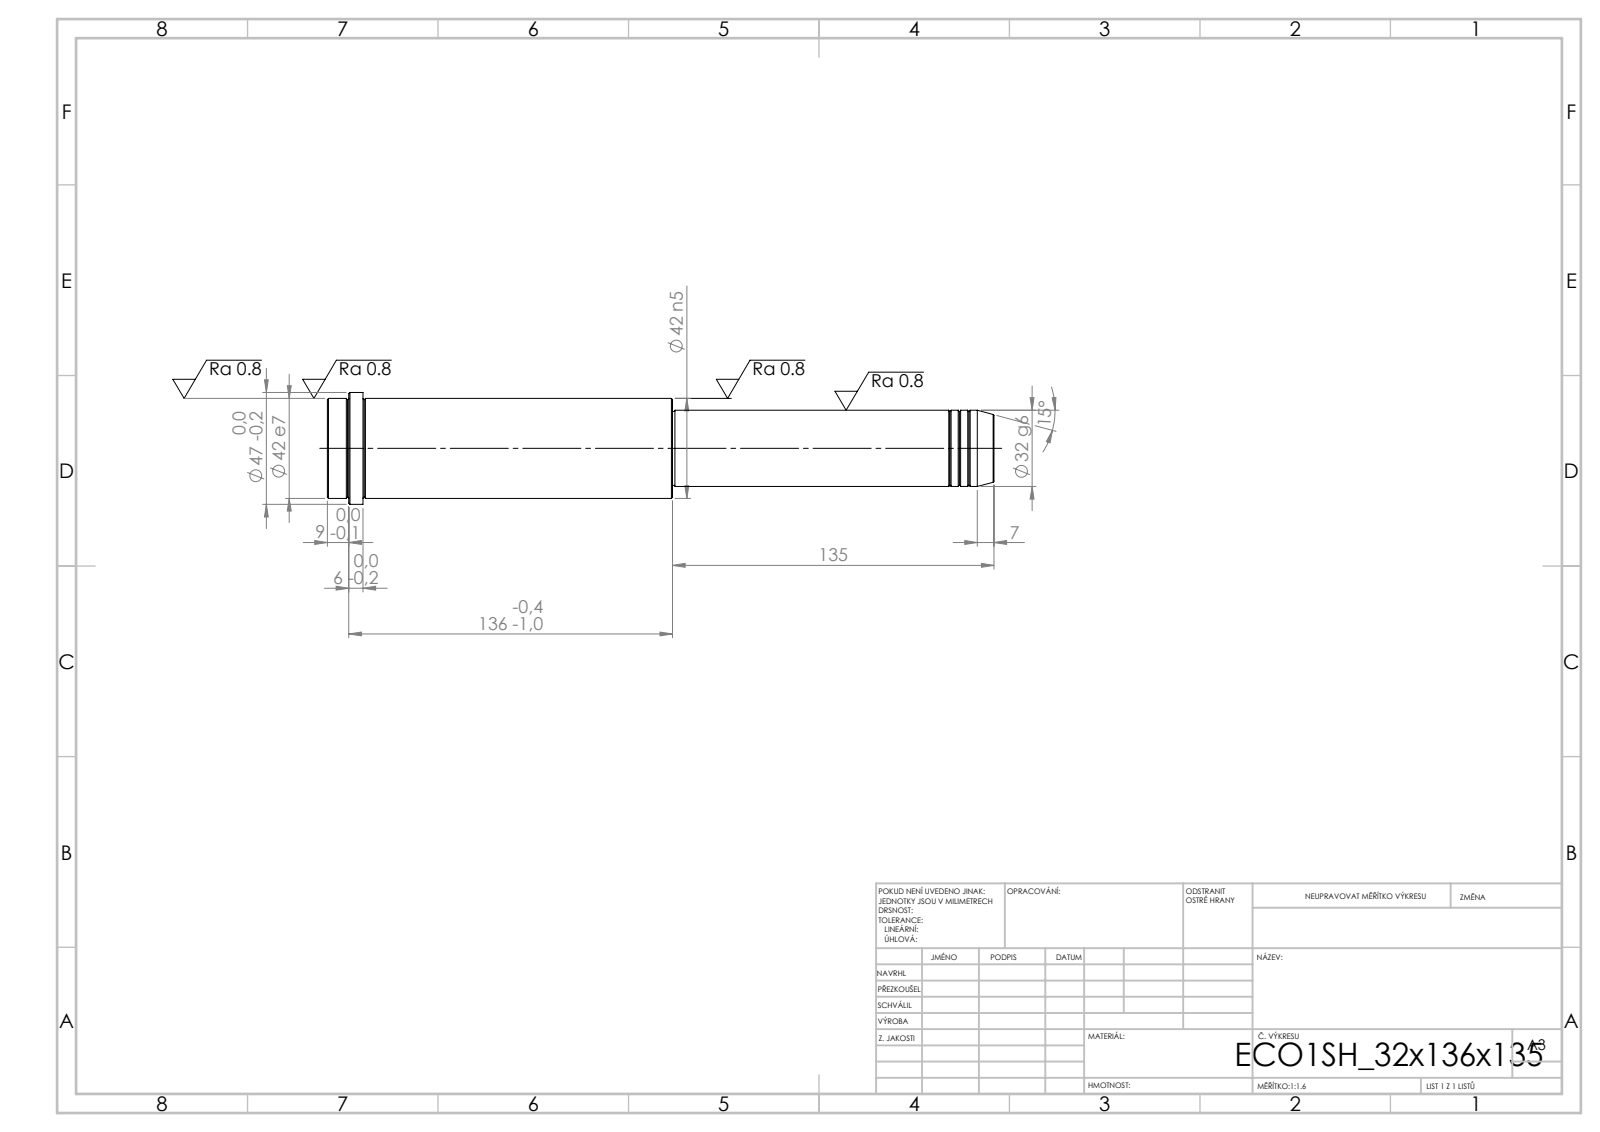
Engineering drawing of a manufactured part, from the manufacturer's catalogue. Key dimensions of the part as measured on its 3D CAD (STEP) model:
STEP written by: SolidWorks 2019 (CONFIG_CONTROL_DESIGN)
Units: millimetres
Bodies: 1 solid, 52 faces (6 planar, 16 cylindrical, 30 other)
Overall size (bounding box): 280 × 47 × 47
Volume: 310 603 mm³ · Surface area: 36 344 mm²
Round bosses / shafts (diameter × count): ⌀47 ×1, ⌀42 ×1, ⌀32 ×1, ⌀31 ×1
Main face-to-face distances: 280, 135, 145, 265, 130, 15, 271, 136, 6, 9
